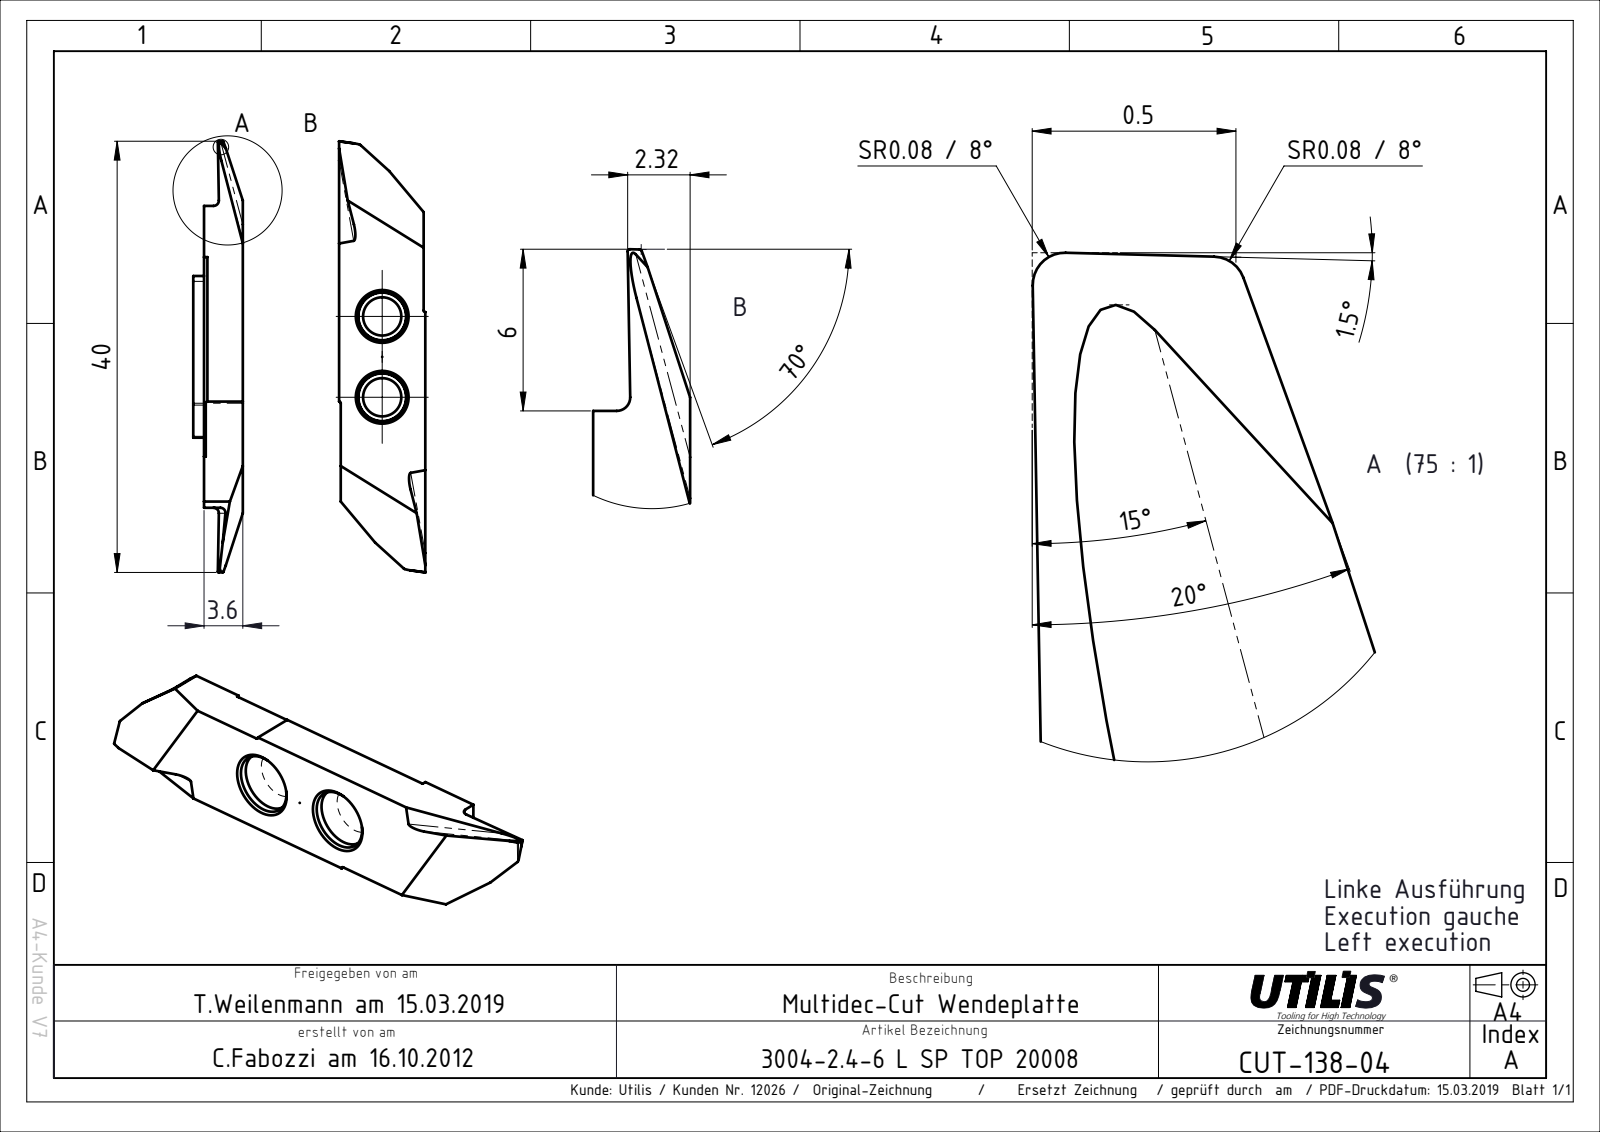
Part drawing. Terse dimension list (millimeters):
name: CUT-138-04
written by: SolidWorks 2022 (AUTOMOTIVE_DESIGN)
unit: mm
bodies: 1 solid, 42 faces (26 planar, 16 cylindrical, 0 other)
size: 40 × 8 × 3.6
volume: 756 mm³; area: 855 mm²
holes: 2× ⌀4.9
rounds: 2× R0.15, 2× R0.5
face distances: 3.6, 8, 7.84, 7.69, 7.85, 23.17, 28, 4.75, 23.25, 39.98
hole spacings: 3.75, 7.5
